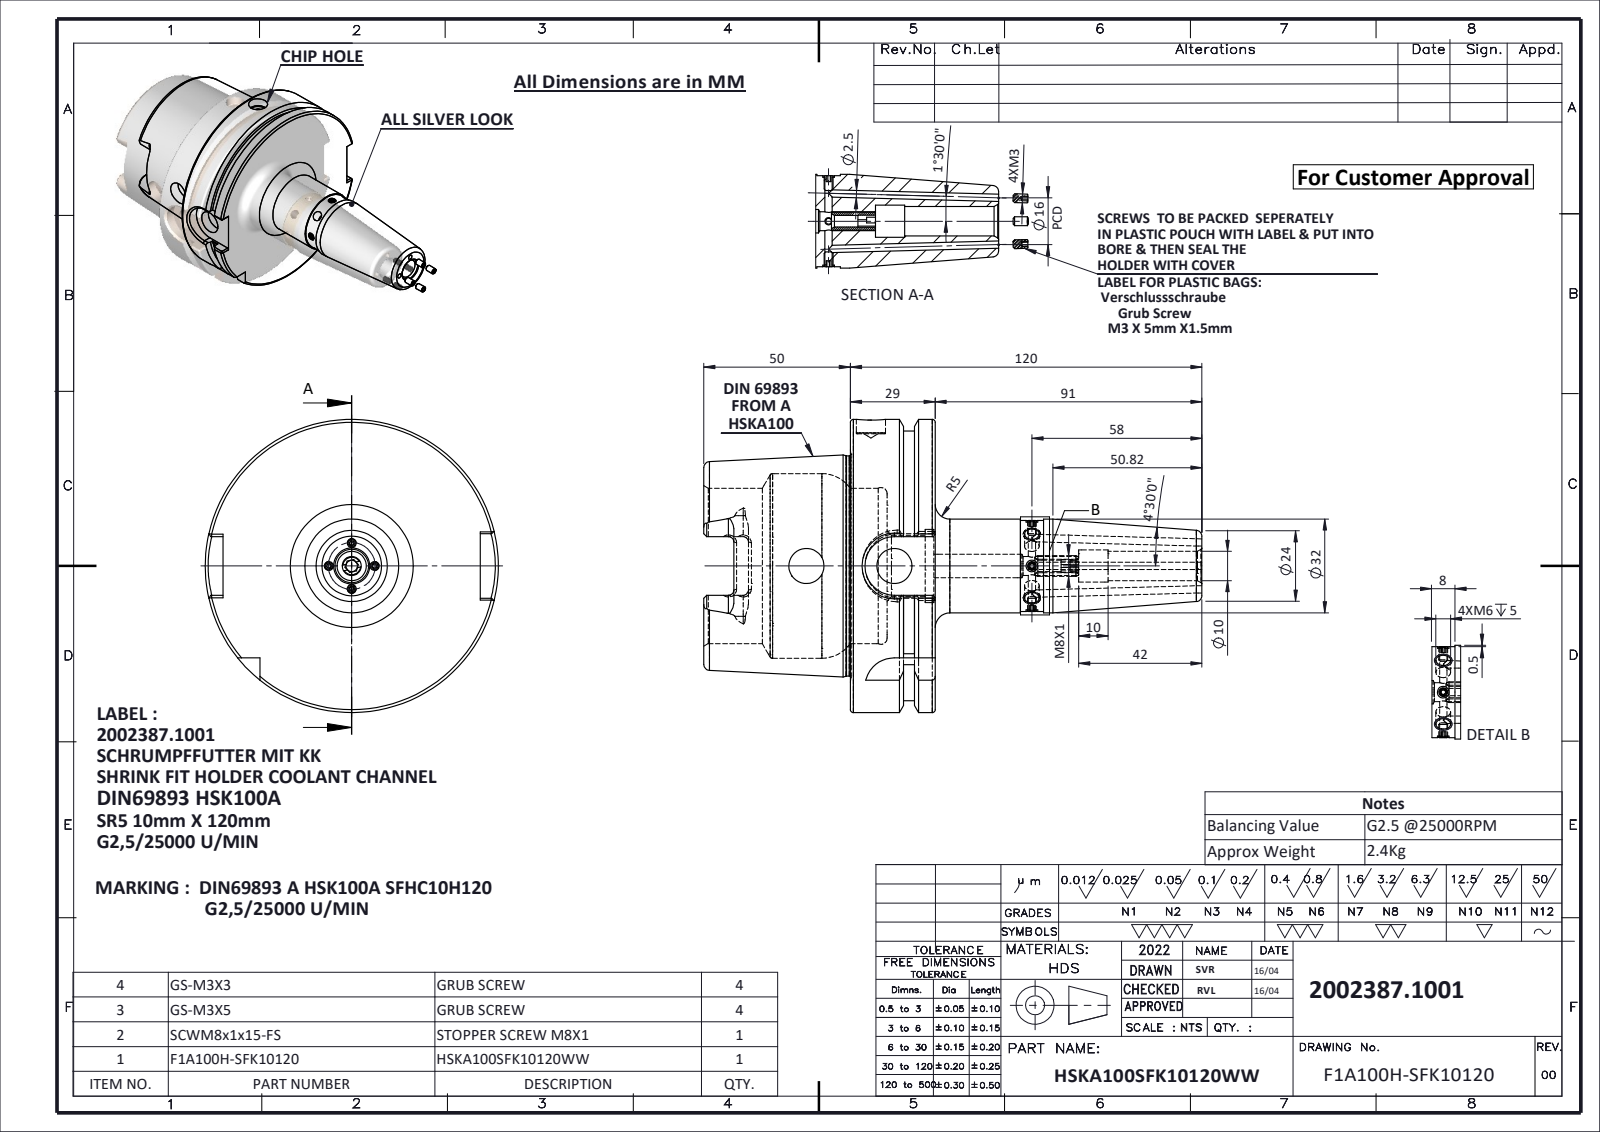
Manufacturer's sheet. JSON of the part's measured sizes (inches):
{"part_name": "GS-M3X5; socket set screw flat point_din_DIN 913 - M3 x 5-N; F1A100H-SFK10120; SCWM8x1x15-DOUBLE FLAT & SLOT (+1 more)", "step_written_by": "SolidWorks 2024 (CONFIG_CONTROL_DESIGN)", "units": "inches", "bodies": {"solids": 10, "faces": 413, "planar": 173, "cylindrical": 118, "other": 122}, "overall_size": [7.086, 3.937, 3.937], "volume_in3": 18.96, "surface_area_in2": 99.1, "round_holes": [[0.098, 6], [0.197, 4], [0.157, 2], [0.394, 2], [0.472, 2], [0.154, 1], [0.256, 1], [0.315, 1], [0.433, 1], [0.827, 1], [0.984, 1], [2.087, 1]], "round_bosses_or_shafts": [[0.118, 6], [3.937, 1], [3.622, 1], [2.959, 1], [1.26, 1], [1.22, 1]], "partial_cylinders_radius": [[0.071, 6], [0.192, 4], [0.394, 2], [0.433, 1]], "face_to_face_distances": [1.14, 0.492, 0.648, 1.969, 2.461, 3.108, 1.122, 0.63, 3.091, 0.018], "hole_center_spacings": [1.181, 1.848, 2.163, 3.03]}
